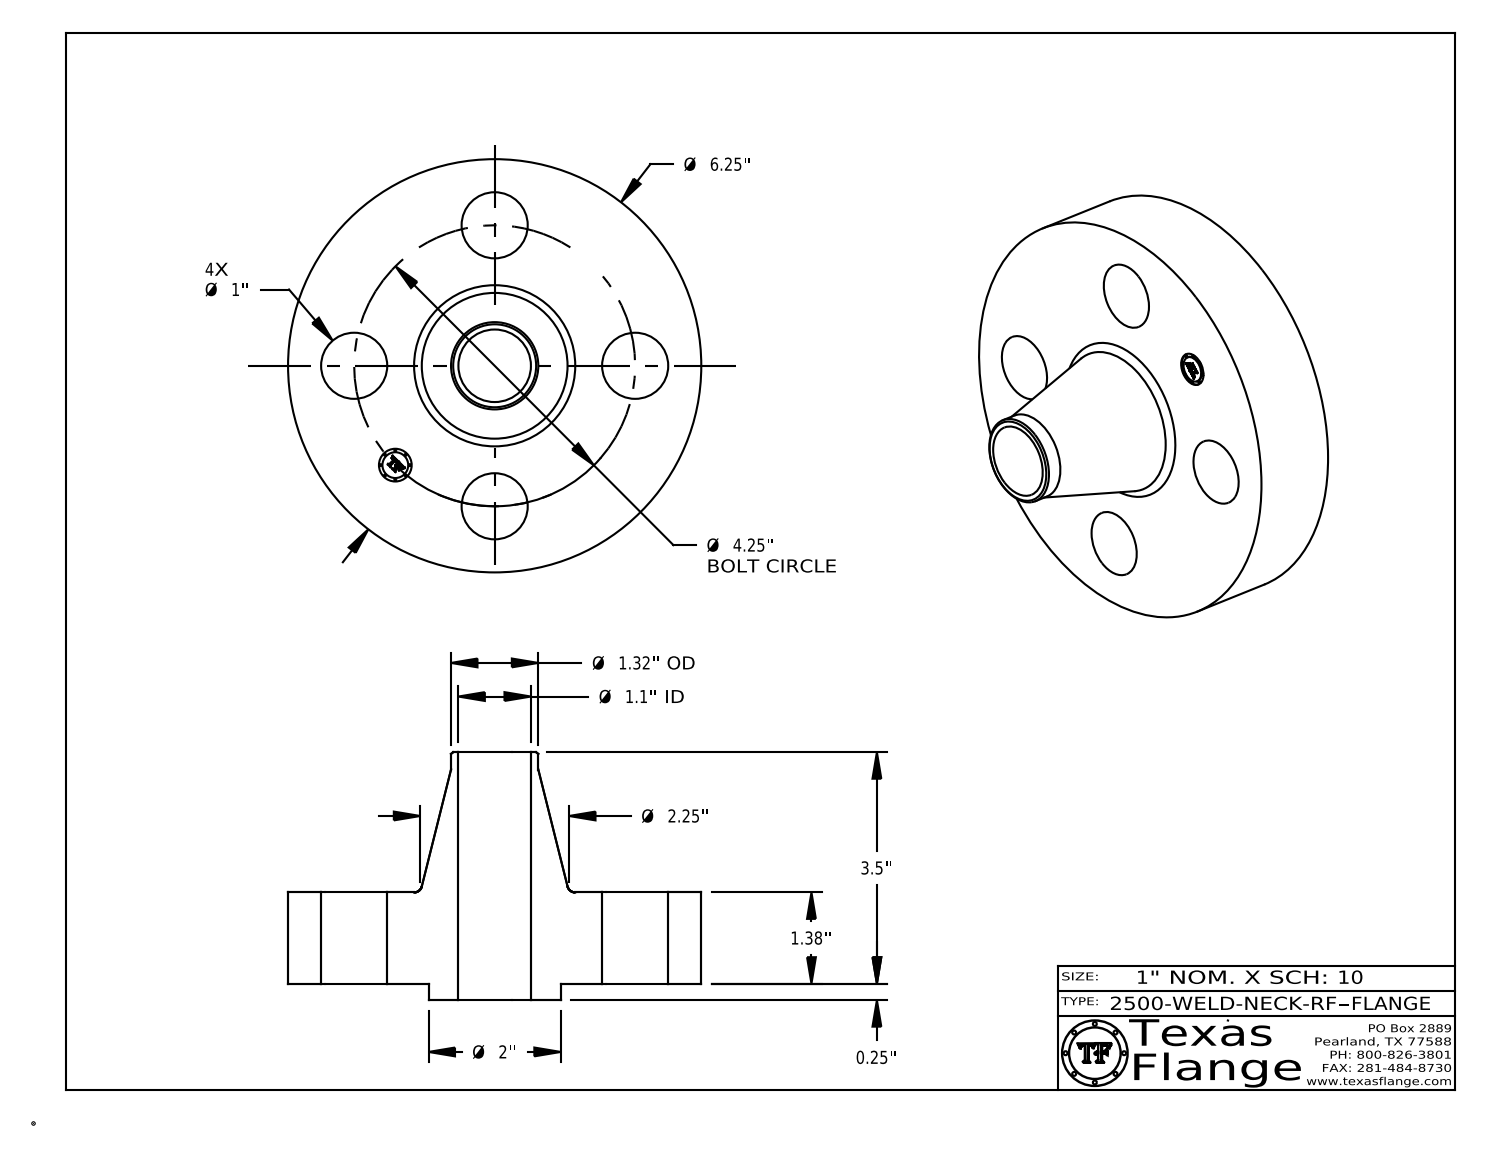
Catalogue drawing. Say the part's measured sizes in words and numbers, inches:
The part is named "2500-WELD-NECK-RF". Its 3-D file was written by "CATIA V5 STEP AP214 (AUTOMOTIVE_DESIGN)". It is 1 solid with 411 faces: 369 planar, 36 cylindrical and 6 other. Overall it measures 6.25 by 6.25 by 3.75 inches. Its volume is 40.37 cubic inches and its surface area 121.2 square inches. Round holes: 4 of diameter 1, 1 of diameter 0.495, 1 of diameter 1.097. Round bosses or shafts: 8 of diameter 0.03, 1 of diameter 6.25, 1 of diameter 2, 1 of diameter 1.32, 1 of diameter 0.39. The main face-to-face distances are 1.38, 0.25, 1.63, 3.75, 3.5, 2.12, 1.615, 1.365, 0.015, 2.135. The hole center spacings are 2.125, 3.006, 1.626, 3.927, 4.25.
